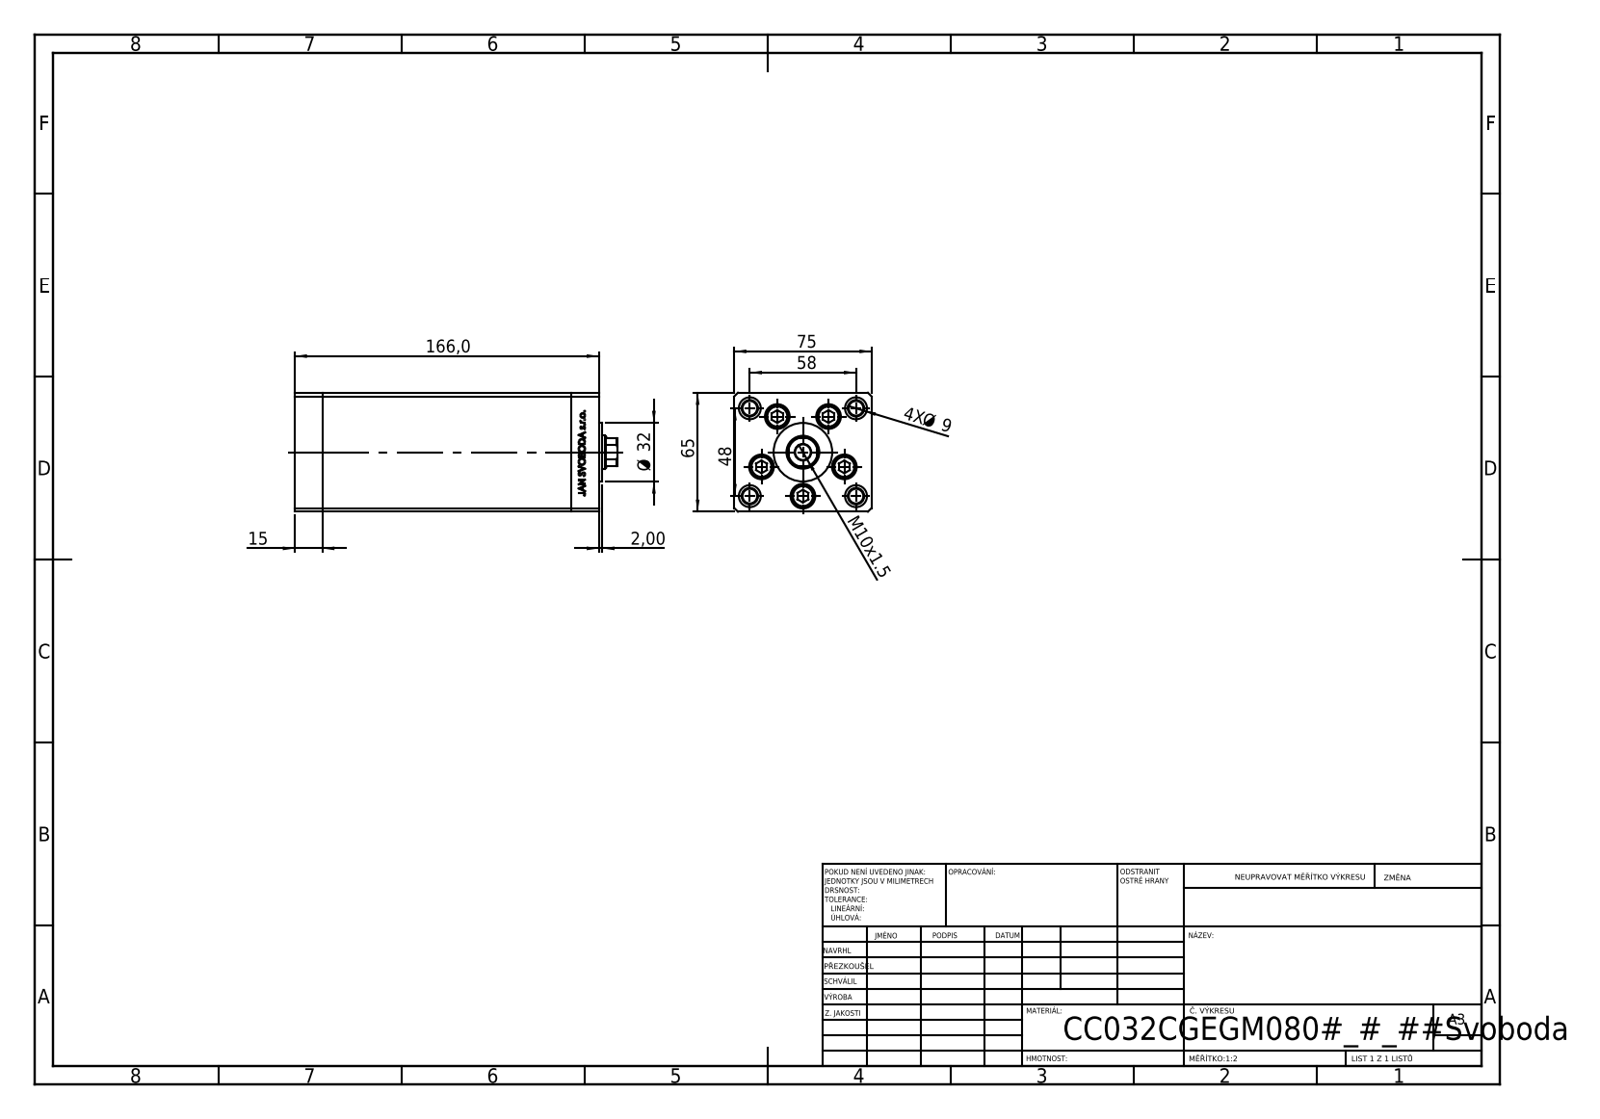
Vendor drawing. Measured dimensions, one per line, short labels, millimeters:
name: V220C BACK_C; V220C_VC_C; ALLEN BOLT; V220C FRONT (+1 more)
written by: SolidWorks 2019 (CONFIG_CONTROL_DESIGN)
unit: mm
bodies: 13 solids, 1159 faces (538 planar, 159 cylindrical, 462 other)
size: 176 × 75 × 65
volume: 684 102 mm³; area: 141 321 mm²
holes: 9× ⌀9, 5× ⌀13.5, 4× ⌀8, 4× ⌀12, 1× ⌀8.5, 1× ⌀12.5, 1× ⌀18
bosses: 5× ⌀8, 4× ⌀12.5, 1× ⌀32
rounds: 2× R0.93, 1× R8.5
face distances: 75, 65, 15, 136, 151, 166, 28, 142, 9, 54.5
hole spacings: 24, 37.64, 15.67, 17.22, 27.71, 28.83, 29, 32.63
